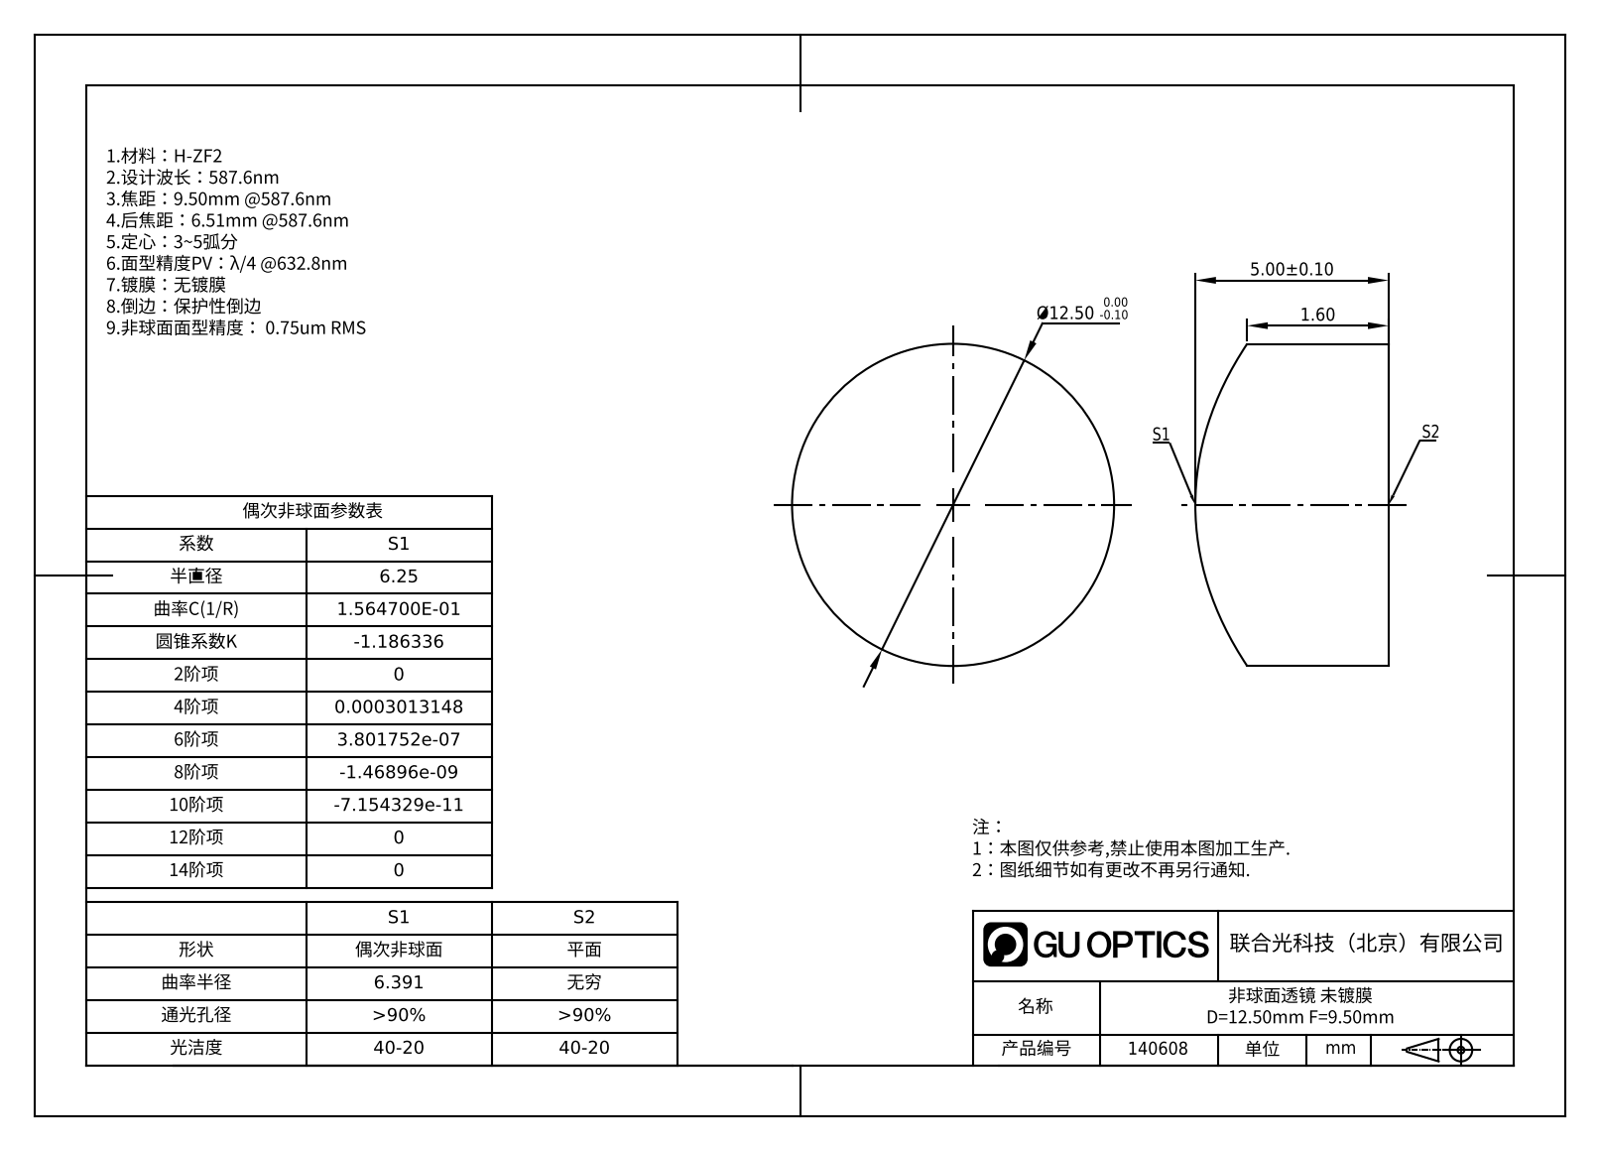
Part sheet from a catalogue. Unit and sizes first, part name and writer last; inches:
Units: inches
Overall size (bounding box): 0.492 × 0.492 × 0.197
Round bosses / shafts (diameter × count): ⌀0.492 ×1
Volume: 0.025 in³ · Surface area: 0.529 in²
Bodies: 1 solid, 5 faces (1 planar, 2 cylindrical, 2 other)
Part name (STEP PRODUCT): surfaces 1,2.stp; GLA11-012-9.5; GLA11-012-9.5.stp
STEP written by: SolidWorks 2023 (CONFIG_CONTROL_DESIGN)
